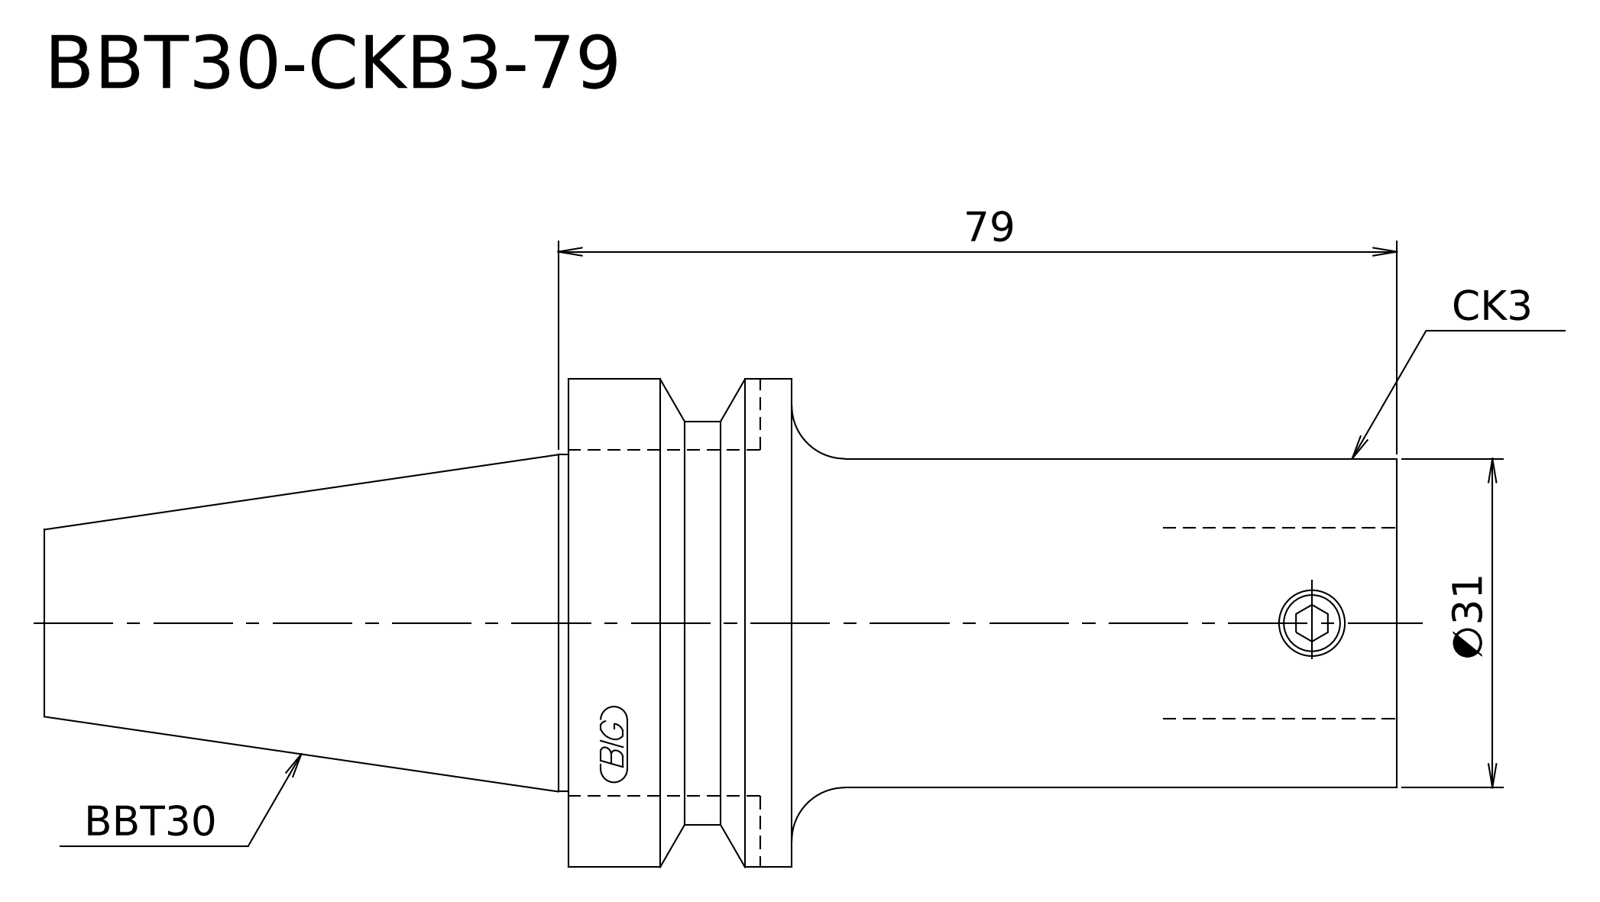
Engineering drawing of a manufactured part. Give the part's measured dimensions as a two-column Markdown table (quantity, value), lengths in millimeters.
| quantity | value |
| --- | --- |
| STEP written by | Kubotek KeyCreator 2011 V10.0.2 (22737) (automotive_design) |
| units | millimeters |
| bodies | 1 solid, 13 faces (4 planar, 5 cylindrical, 4 other) |
| overall size | 127.4 × 46 × 46 |
| volume | 100 826 mm³ |
| surface area | 15 470 mm² |
| round bosses / shafts (diameter × count) | 46 × 1, 38 × 1, 31.75 × 1, 31 × 1 |
| main face-to-face distances | 78, 57, 21, 127.4, 70.4, 49.4 |
